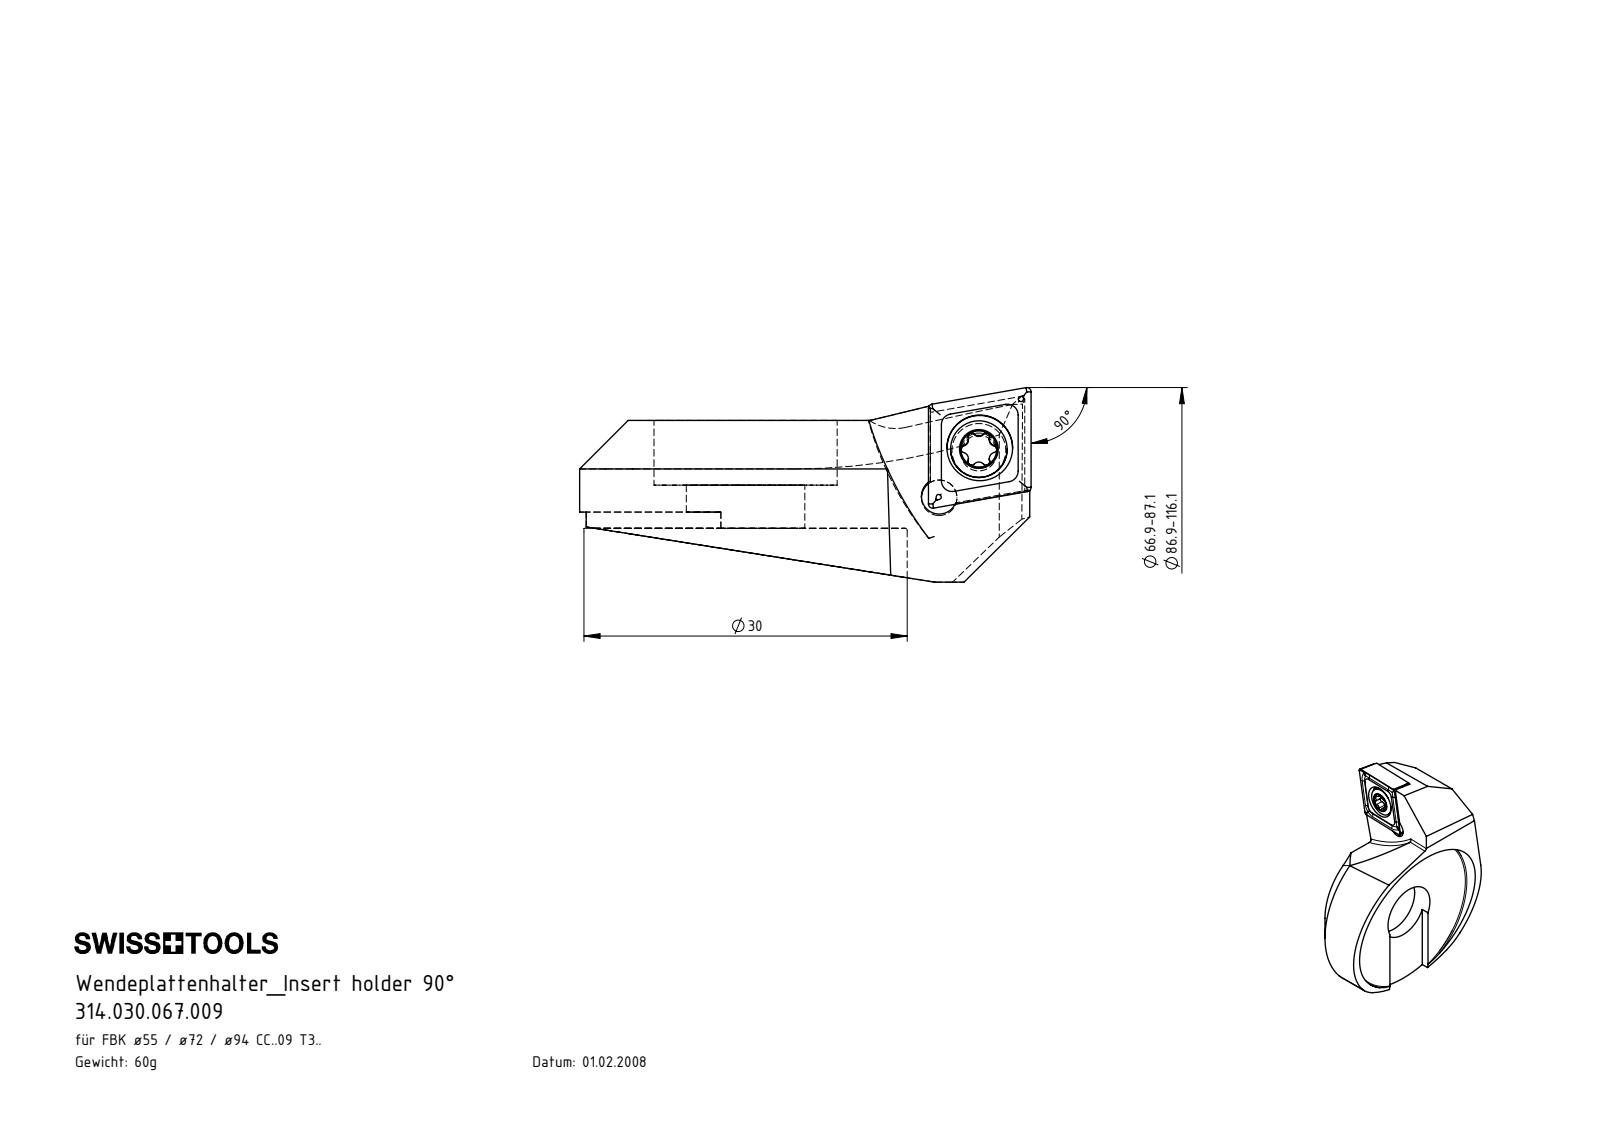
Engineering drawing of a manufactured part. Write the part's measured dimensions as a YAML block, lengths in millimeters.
part_name: "WCA-ER2.001.005_A; CCMT060204; 314.030.067.009; F55-WCA.001.013_D_fertigbearbeitet"
step_written_by: "SolidWorks 2017 (CONFIG_CONTROL_DESIGN)"
units: millimeters
bodies: {solids: 5, faces: 153, planar: 48, cylindrical: 48, other: 57}
overall_size: [41.9, 33.1, 18.05]
volume: 8032
surface_area: 4569
round_holes:
  - {diameter: 2.05, count: 1}
  - {diameter: 2.1, count: 1}
  - {diameter: 2.8, count: 1}
  - {diameter: 3.85, count: 1}
  - {diameter: 11, count: 1}
  - {diameter: 17, count: 1}
  - {diameter: 30, count: 1}
round_bosses_or_shafts:
  - {diameter: 3.4, count: 1}
  - {diameter: 2.5, count: 1}
partial_cylinders:
  - {radius: 0.21, count: 6}
  - {radius: 0.36, count: 5}
  - {radius: 0.5, count: 2}
  - {radius: 10, count: 2}
  - {radius: 0.36, count: 1}
  - {radius: 1.05, count: 1}
  - {radius: 5, count: 1}
  - {radius: 16.55, count: 1}
face_to_face_distances: [10, 9, 1, 5, 6, 4, 8.5, 7.5, 2.5, 1.5]
hole_center_spacings: [3.91, 4.04]
